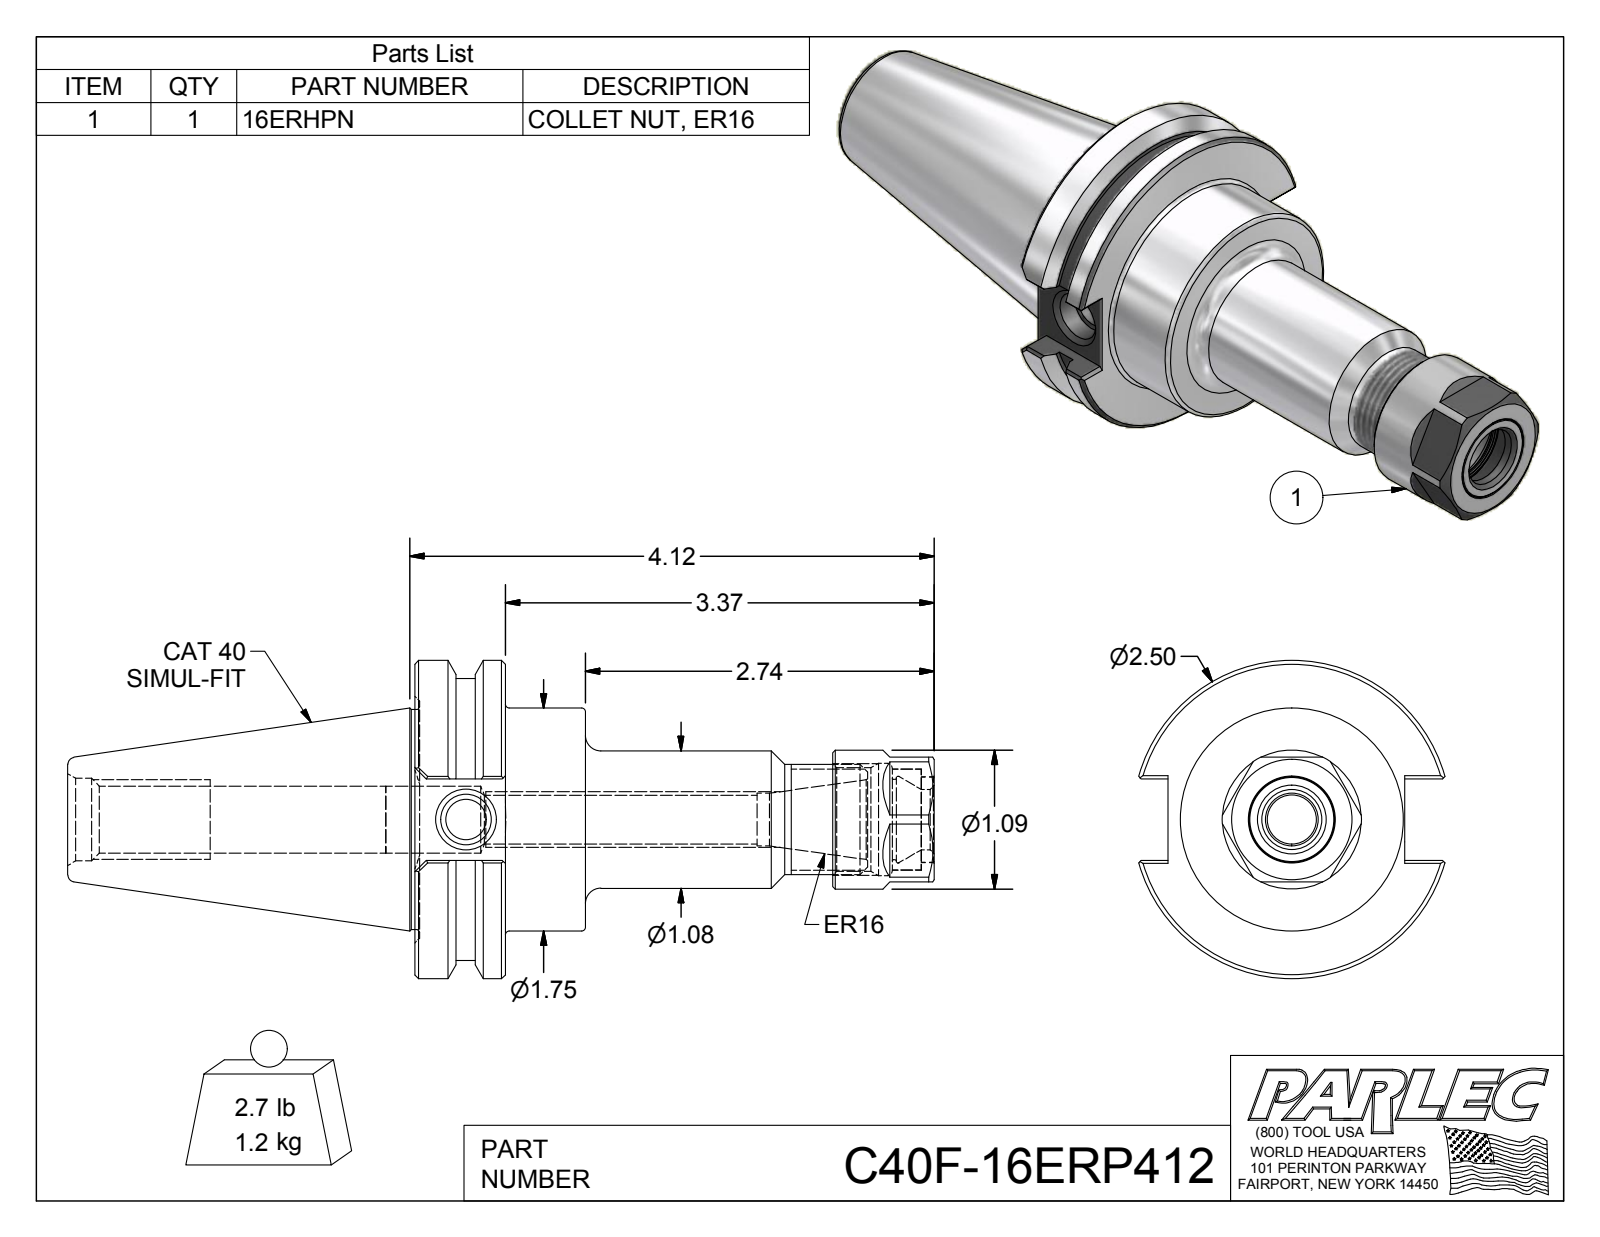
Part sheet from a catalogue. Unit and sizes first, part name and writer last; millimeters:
Units: millimetres
Overall size (bounding box): 172.9 × 63.5 × 61.1
Round holes (diameter × count): ⌀8 ×1, ⌀9.7 ×1, ⌀10.1 ×1, ⌀10.5 ×1, ⌀12 ×1, ⌀13.4 ×1, ⌀13.4 ×1, ⌀16 ×1, ⌀16.5 ×1, ⌀17.1 ×1, ⌀17.3 ×1, ⌀20.2 ×1
Round bosses / shafts (diameter × count): ⌀63.5 ×1, ⌀56.3 ×1, ⌀44.5 ×1, ⌀43.9 ×1, ⌀27.7 ×1, ⌀27.4 ×1, ⌀22 ×1, ⌀20.1 ×1
Main face-to-face distances: 18.1, 34.1, 16, 24.9, 103.7, 85.6, 69.6, 47.2, 83.4, 65.4
Volume: 157 000 mm³ · Surface area: 34 240 mm²
Bodies: 3 solids, 124 faces (54 planar, 27 cylindrical, 43 other)
Part name (STEP PRODUCT): C40F-16ERP412; C40F-16ER4-1; 16ERHPN
STEP written by: Autodesk Inventor 2012 (AUTOMOTIVE_DESIGN)
